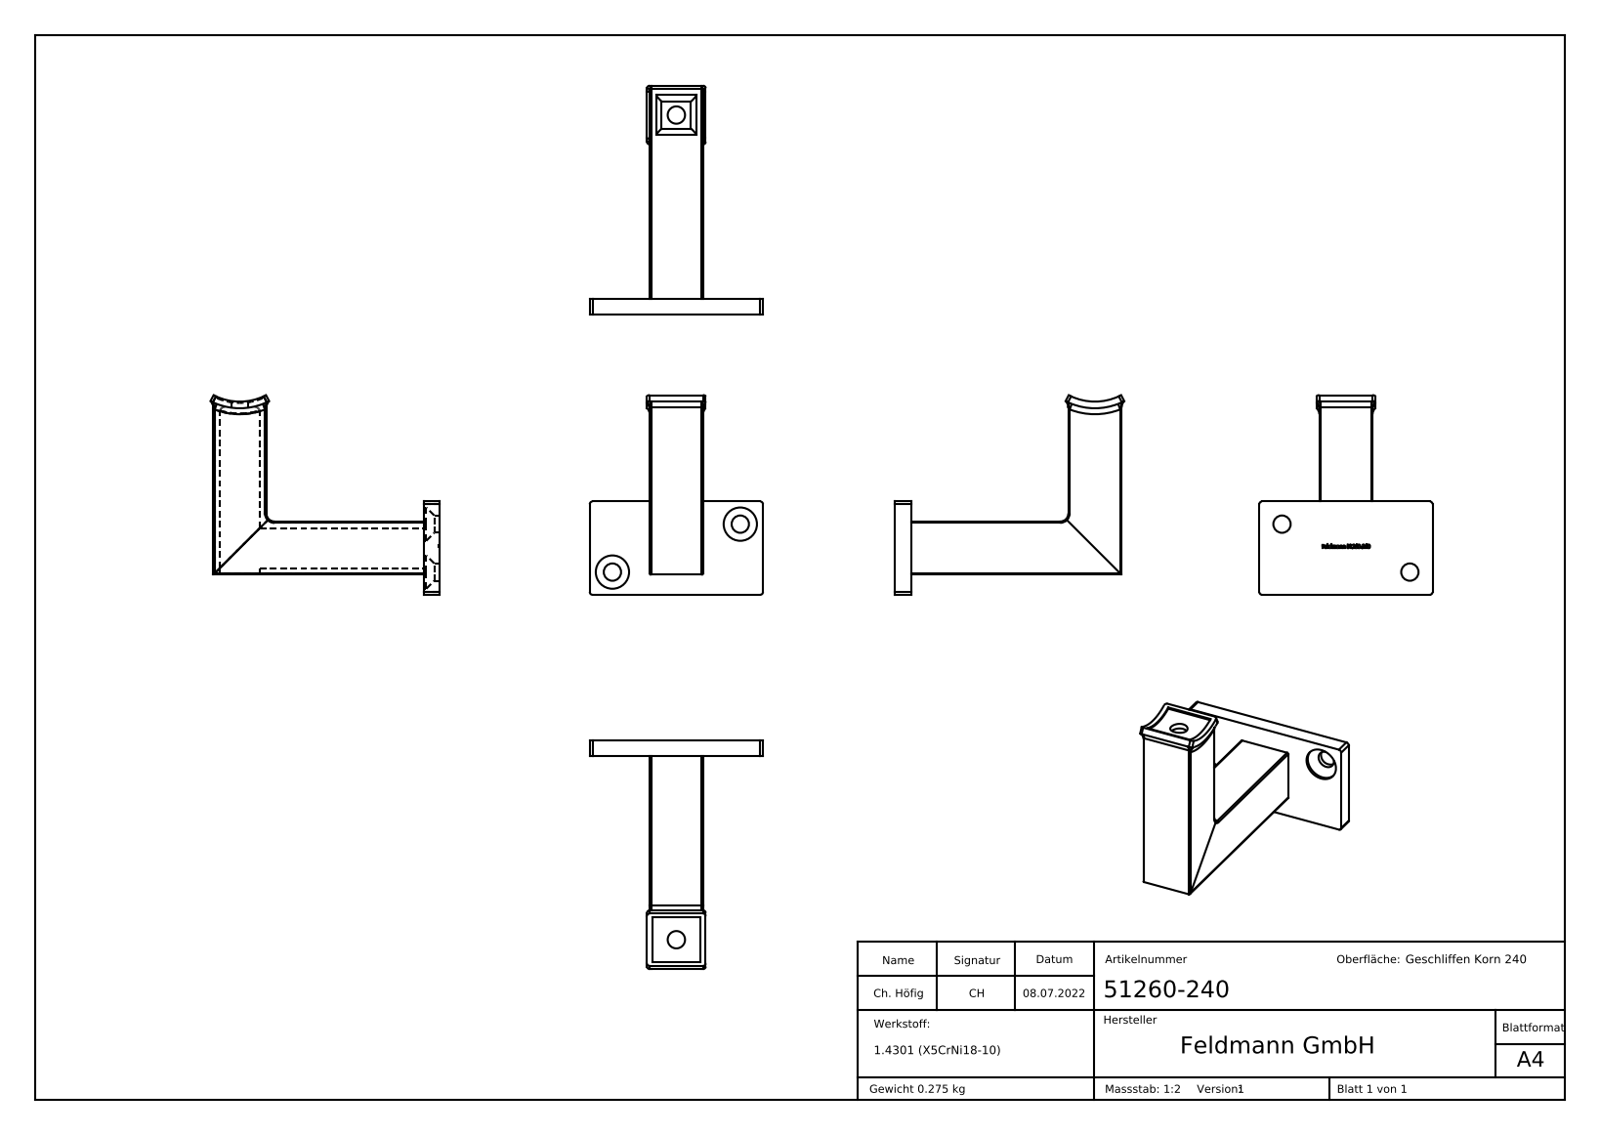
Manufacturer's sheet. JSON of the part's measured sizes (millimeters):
{"part_name": "51260-240", "step_written_by": "SolidWorks 2018 (CONFIG_CONTROL_DESIGN)", "units": "millimeters", "bodies": {"solids": 1, "faces": 300, "planar": 154, "cylindrical": 29, "other": 117}, "overall_size": [86, 74.92, 65], "volume_mm3": 34815, "surface_area_mm2": 23338, "round_holes": [[6.5, 3], [12.5, 2]], "partial_cylinders_radius": [[0.5, 8], [1, 8], [3, 3], [2, 2], [21.2, 1], [21.7, 1], [23.7, 1]], "face_to_face_distances": [2.5, 17.5, 20, 15, 6, 85, 79, 25, 65, 82.5], "hole_center_spacings": [51.26]}
